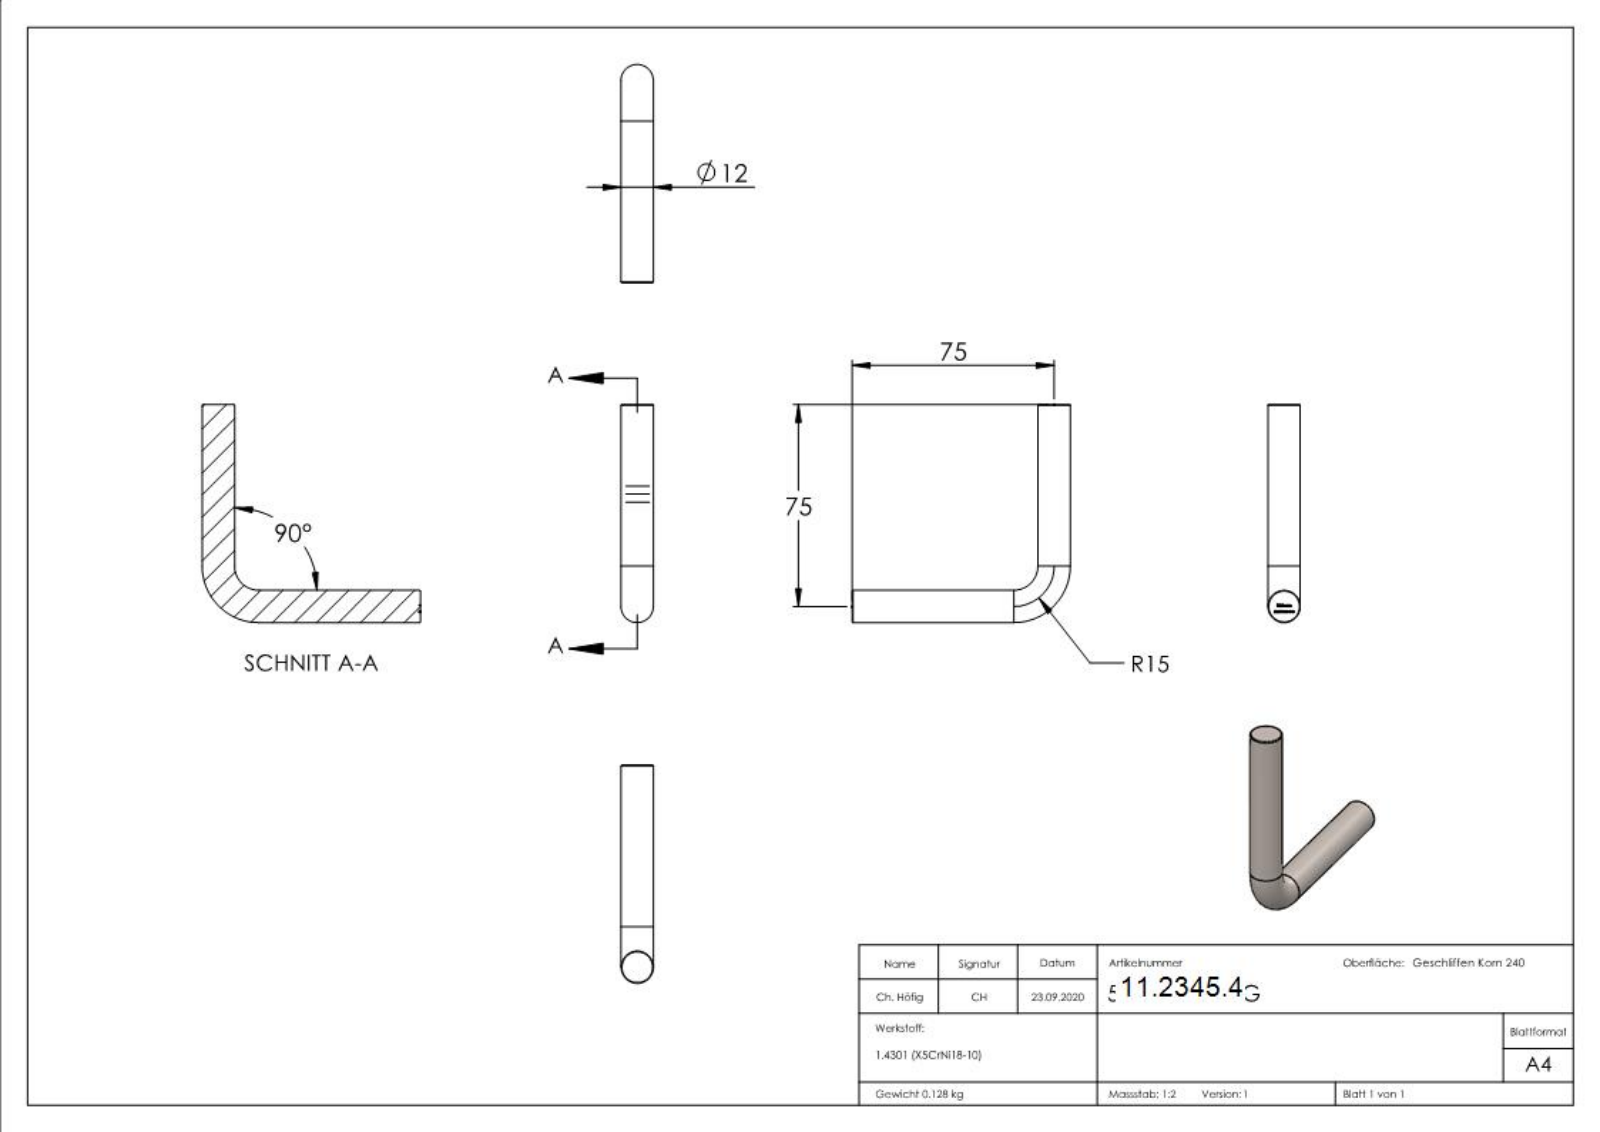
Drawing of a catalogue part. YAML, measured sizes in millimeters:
part_name: "50247-240-OG"
step_written_by: "SolidWorks 2018 (CONFIG_CONTROL_DESIGN)"
units: millimeters
bodies: {solids: 1, faces: 259, planar: 146, cylindrical: 4, other: 109}
overall_size: [81, 81, 12]
volume: 16232
surface_area: 5659
round_bosses_or_shafts:
  - {diameter: 12, count: 2}
face_to_face_distances: [0.5, 2.2, 1.78, 1.04, 0.79, 2.45, 0.67, 0.83, 0.71, 1.88]
